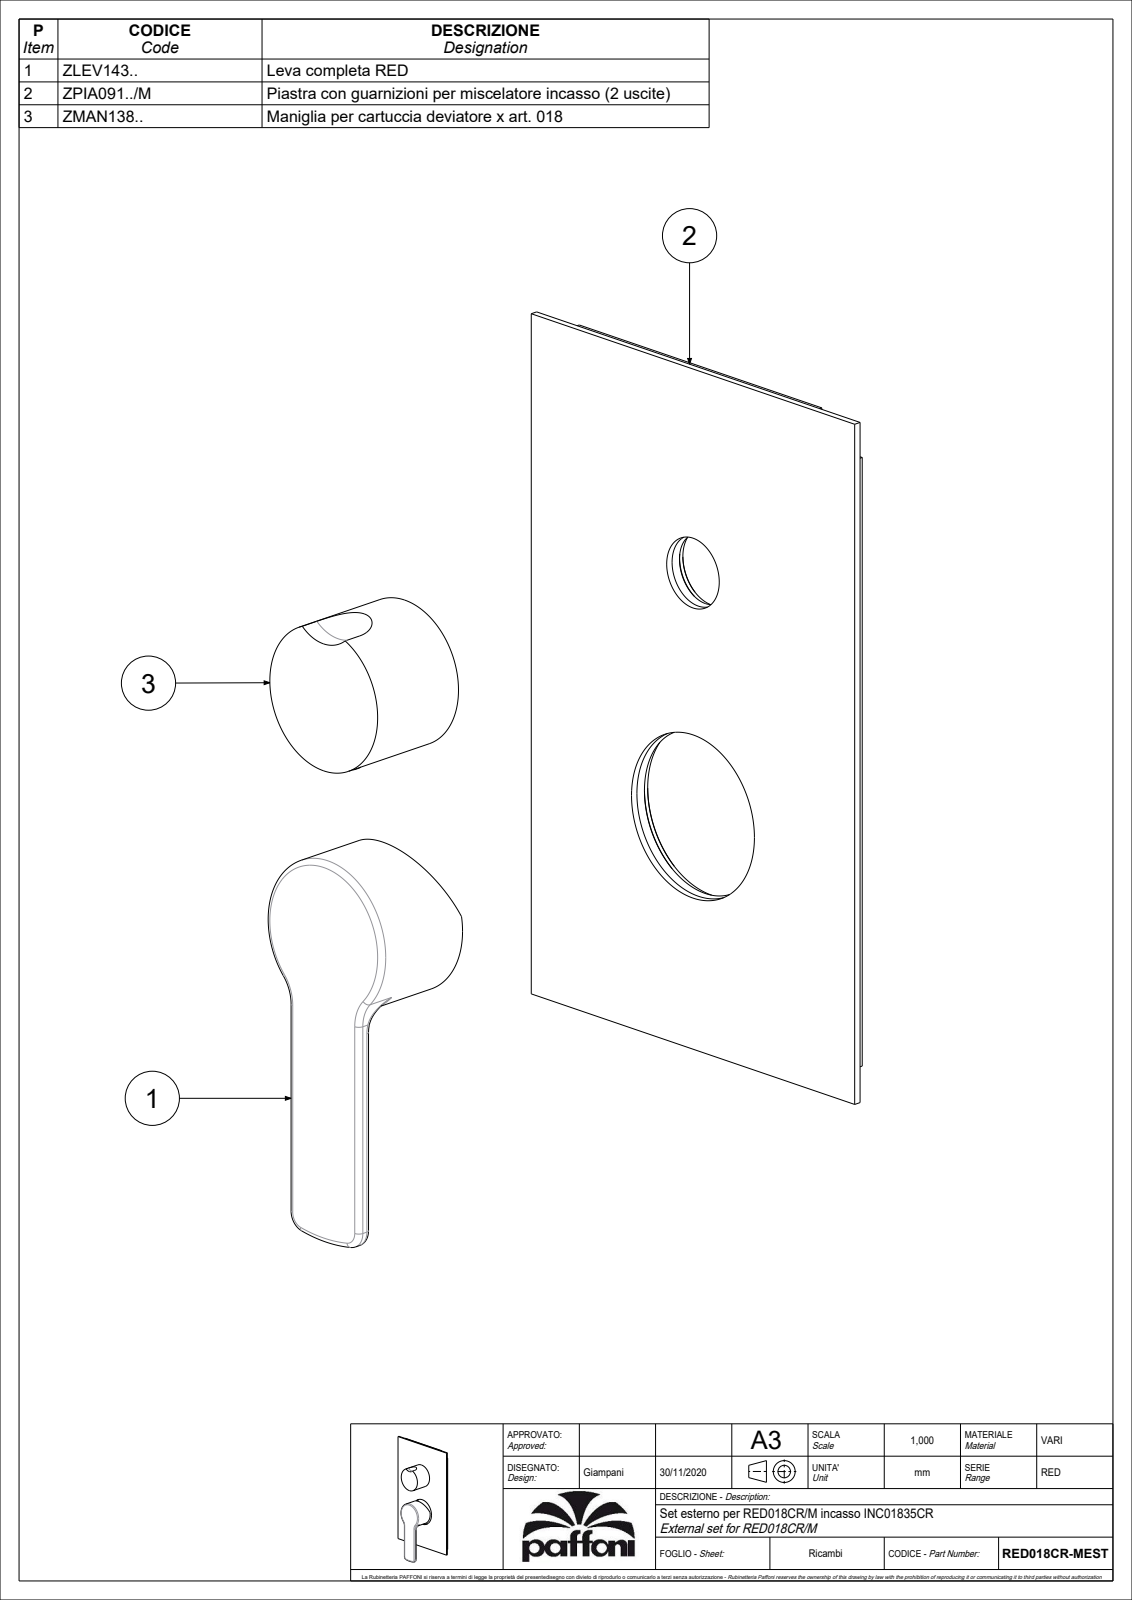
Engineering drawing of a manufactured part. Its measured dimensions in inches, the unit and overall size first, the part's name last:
Units: inches
Overall size (bounding box): 8.228 × 4.724 × 1.569
Round holes (diameter × count): ⌀0.118 ×2, ⌀0.126 ×1, ⌀0.13 ×1, ⌀0.165 ×1, ⌀0.177 ×1, ⌀0.583 ×1, ⌀0.768 ×1, ⌀0.846 ×1, ⌀0.984 ×1, ⌀1.417 ×1, ⌀1.795 ×1, ⌀1.874 ×1
Round bosses / shafts (diameter × count): ⌀0.299 ×2, ⌀0.217 ×2, ⌀2.15 ×1, ⌀1.693 ×1, ⌀1.575 ×1, ⌀1.122 ×1, ⌀0.945 ×1, ⌀0.197 ×1
Partial cylindrical surfaces — rounded edges, fillets, slot ends (radius × count): R0.02 ×39, R0.059 ×4, R0.197 ×2, R0.394 ×2, R0.492 ×1, R1.969 ×1
Main face-to-face distances: 0.079, 0.031, 0.11, 1.193, 1.161, 1.083, 1.339, 1.26, 0.177, 1.37
Hole centre spacings: 0.236, 0.394, 2.677, 3.071
Volume: 5.883 in³ · Surface area: 114.4 in²
Bodies: 3 solids, 360 faces (118 planar, 126 cylindrical, 116 other)
Part name (STEP PRODUCT): RED018CR-MEST
STEP written by: CREO PARAMETRIC BY PTC INC, 2020044 (CONFIG_CONTROL_DESIGN)
